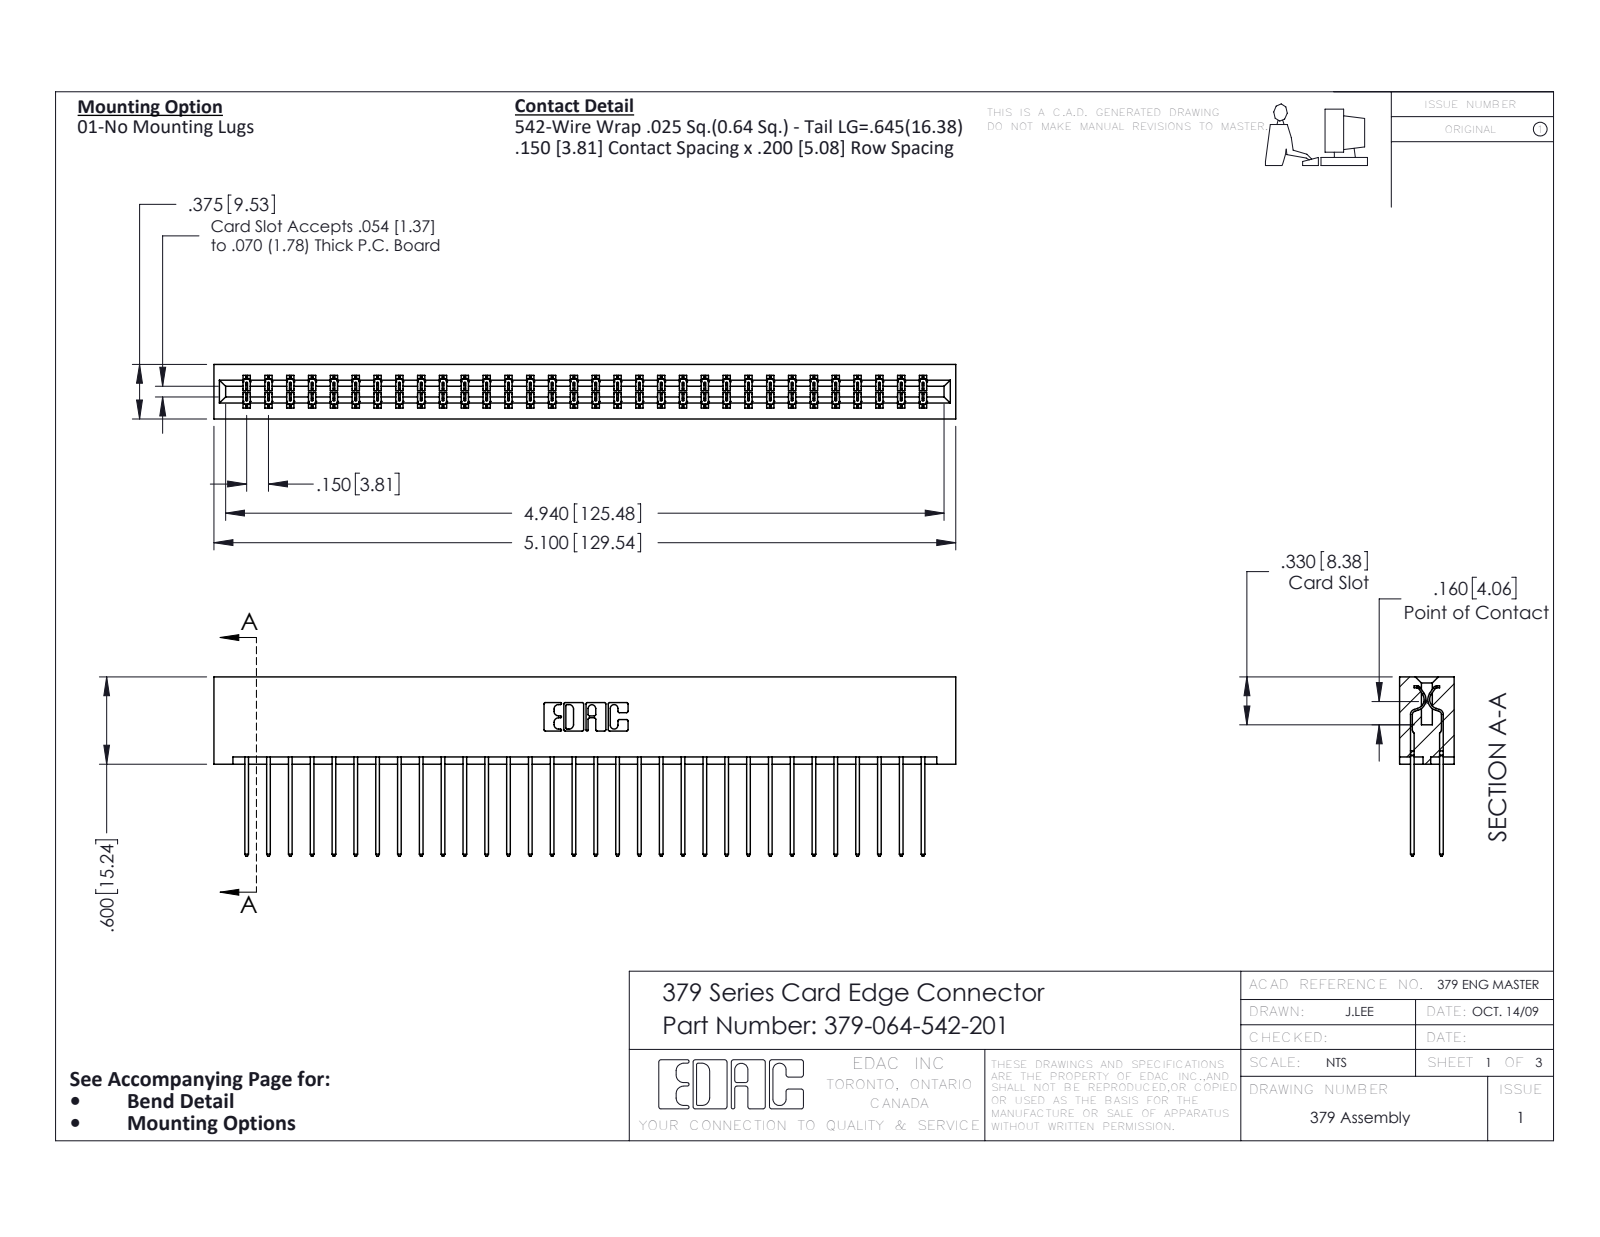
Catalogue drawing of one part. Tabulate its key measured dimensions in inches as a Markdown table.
| quantity | value |
| --- | --- |
| part name | 345-292-001_345-293-142; 379 Part_Lugless; 379-064-542-201 |
| STEP written by | SolidWorks 2016 (CONFIG_CONTROL_DESIGN) |
| units | inches |
| bodies | 65 solids, 3434 faces (2370 planar, 1064 cylindrical, 0 other) |
| overall size | 5.1 × 1.232 × 0.375 |
| volume | 0.898 in³ |
| surface area | 27.85 in² |
| partial cylindrical surfaces (radius × count) | 0.006 × 96, 0.01 × 64, 0.01 × 22, 0.007 × 6, 0.031 × 6, 0.026 × 3, 0.014 × 2, 0.022 × 2 |
| main face-to-face distances | 0.3, 0.075, 0.1, 0.375, 0.2, 0.275, 0.025, 0.076, 0.15, 0.225 |
